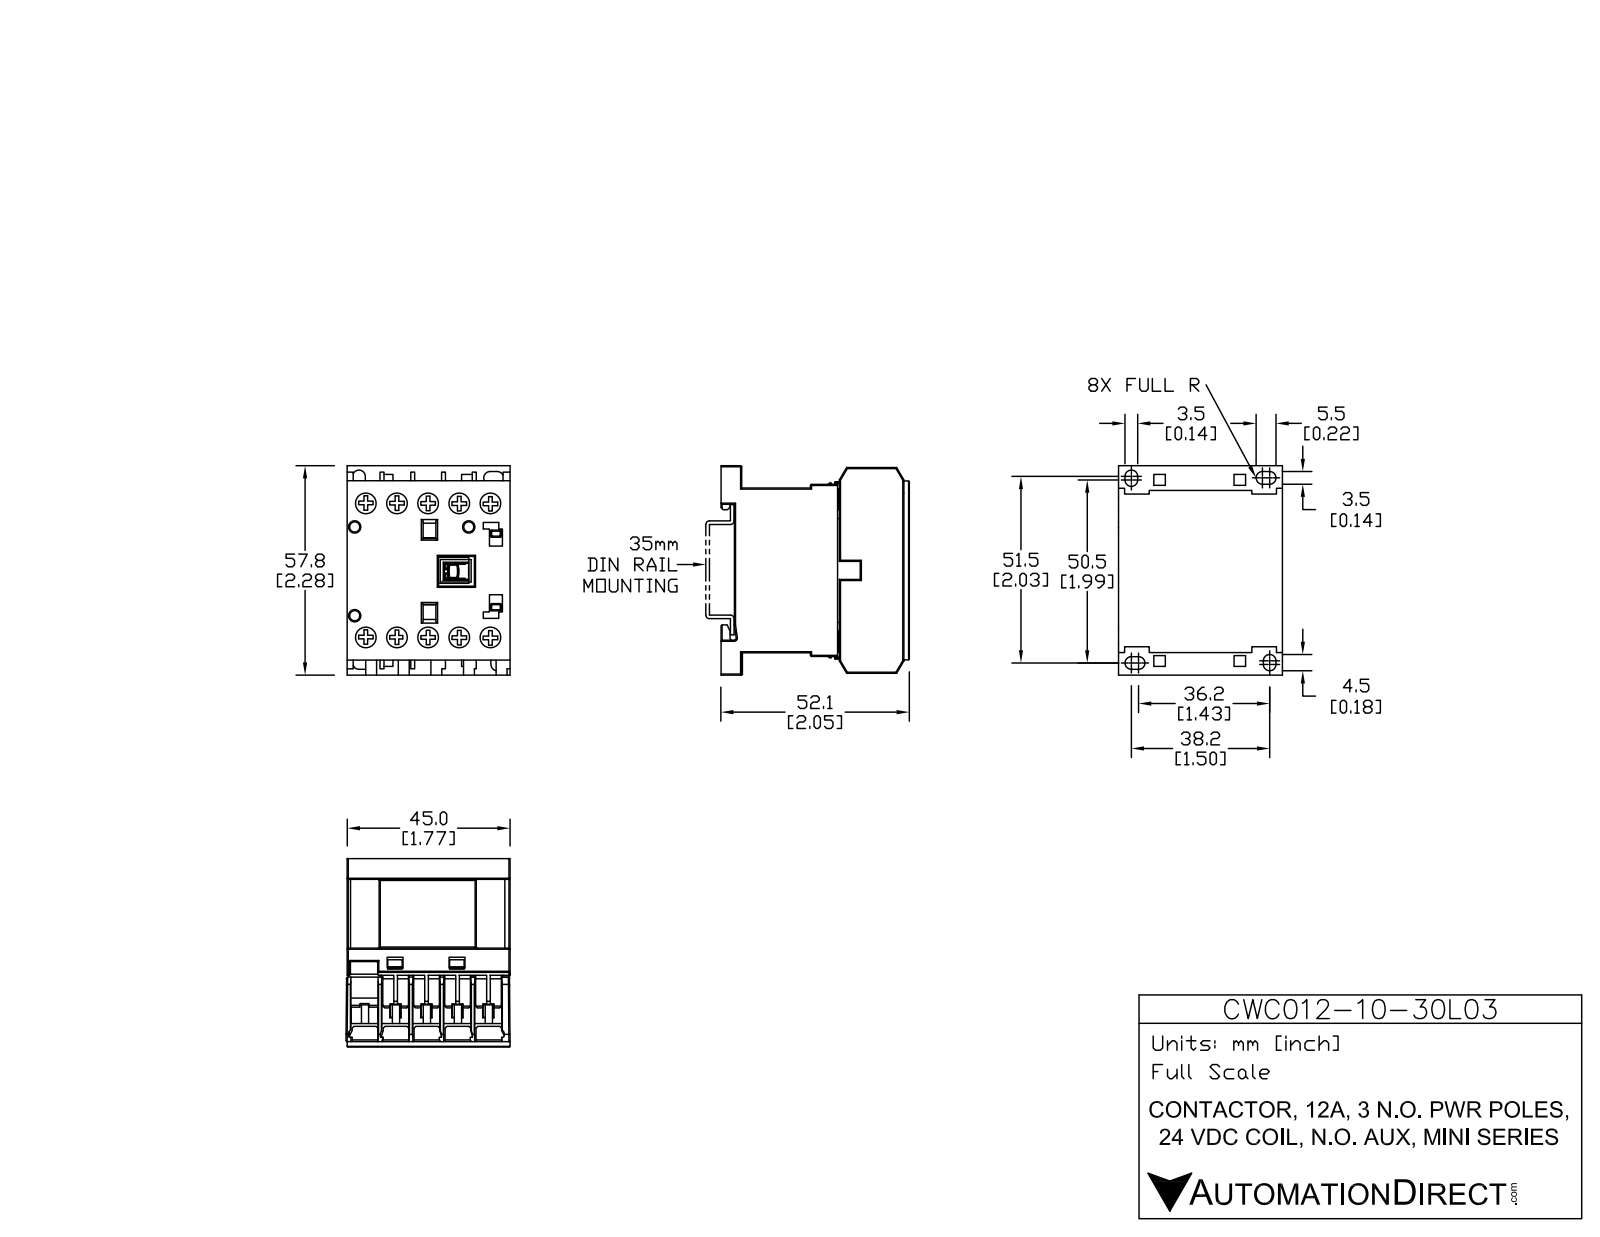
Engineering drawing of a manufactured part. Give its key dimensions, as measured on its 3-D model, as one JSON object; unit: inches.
{"part_name": "CWC12-10-30L03", "step_written_by": "SolidWorks 2013 (AUTOMOTIVE_DESIGN)", "units": "inches", "bodies": {"solids": 15, "faces": 535, "planar": 445, "cylindrical": 90, "other": 0}, "overall_size": [2.285, 2.052, 1.801], "volume_in3": 5.927, "surface_area_in2": 47.18, "round_holes": [[0.244, 10], [0.11, 3]], "round_bosses_or_shafts": [[0.232, 10]], "partial_cylinders_radius": [[0.012, 20], [0.068, 6], [0.068, 2], [0.013, 1], [0.017, 1], [0.022, 1]], "face_to_face_distances": [0.325, 1.791, 0.049, 0.65, 0.374, 0.217, 0.699, 0.202, 0.419, 0.276], "hole_center_spacings": [0.337, 1.494, 0.673, 1.603, 1.455, 1.01, 1.771, 0.272]}
